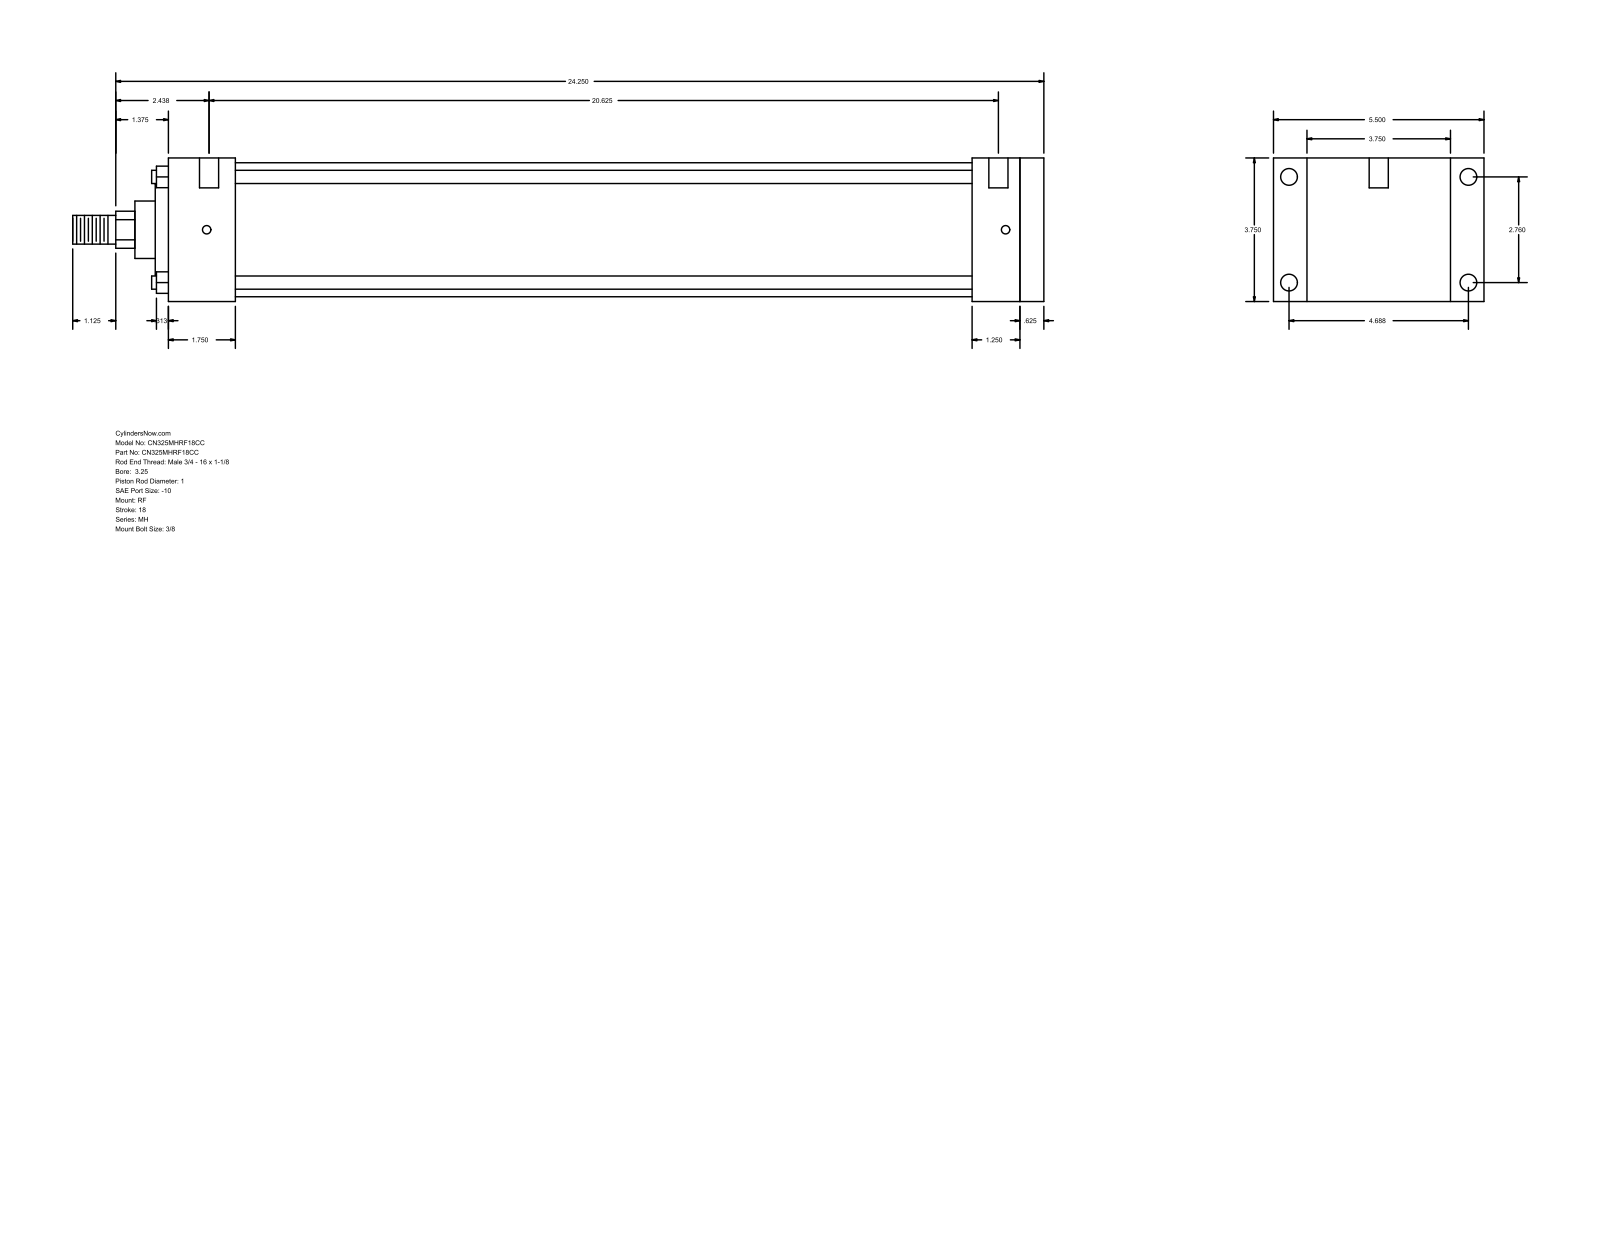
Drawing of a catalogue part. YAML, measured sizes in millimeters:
part_name: "MH_RF__0325_1"
step_written_by: "GSSL Pune (CONFIG_CONTROL_DESIGN)"
units: millimeters
bodies: {solids: 0, faces: 94, planar: 65, cylindrical: 29, other: 0}
overall_size: [644.52, 139.7, 95.25]
round_holes:
  - {diameter: 5.56, count: 4}
  - {diameter: 11.13, count: 4}
  - {diameter: 12.7, count: 2}
round_bosses_or_shafts:
  - {diameter: 8.76, count: 4}
  - {diameter: 88.9, count: 1}
  - {diameter: 60.33, count: 1}
  - {diameter: 38.1, count: 1}
  - {diameter: 25.4, count: 1}
  - {diameter: 19.05, count: 1}
partial_cylinders:
  - {radius: 12.29, count: 1}
face_to_face_distances: [95.24, 581.03, 565.16, 15.87, 22.23, 117.47, 44.46, 520.7, 536.57, 533.41]
hole_center_spacings: [70.1, 119.06, 138.16, 530.22, 1.58, 4.76, 523.88, 525.46]
